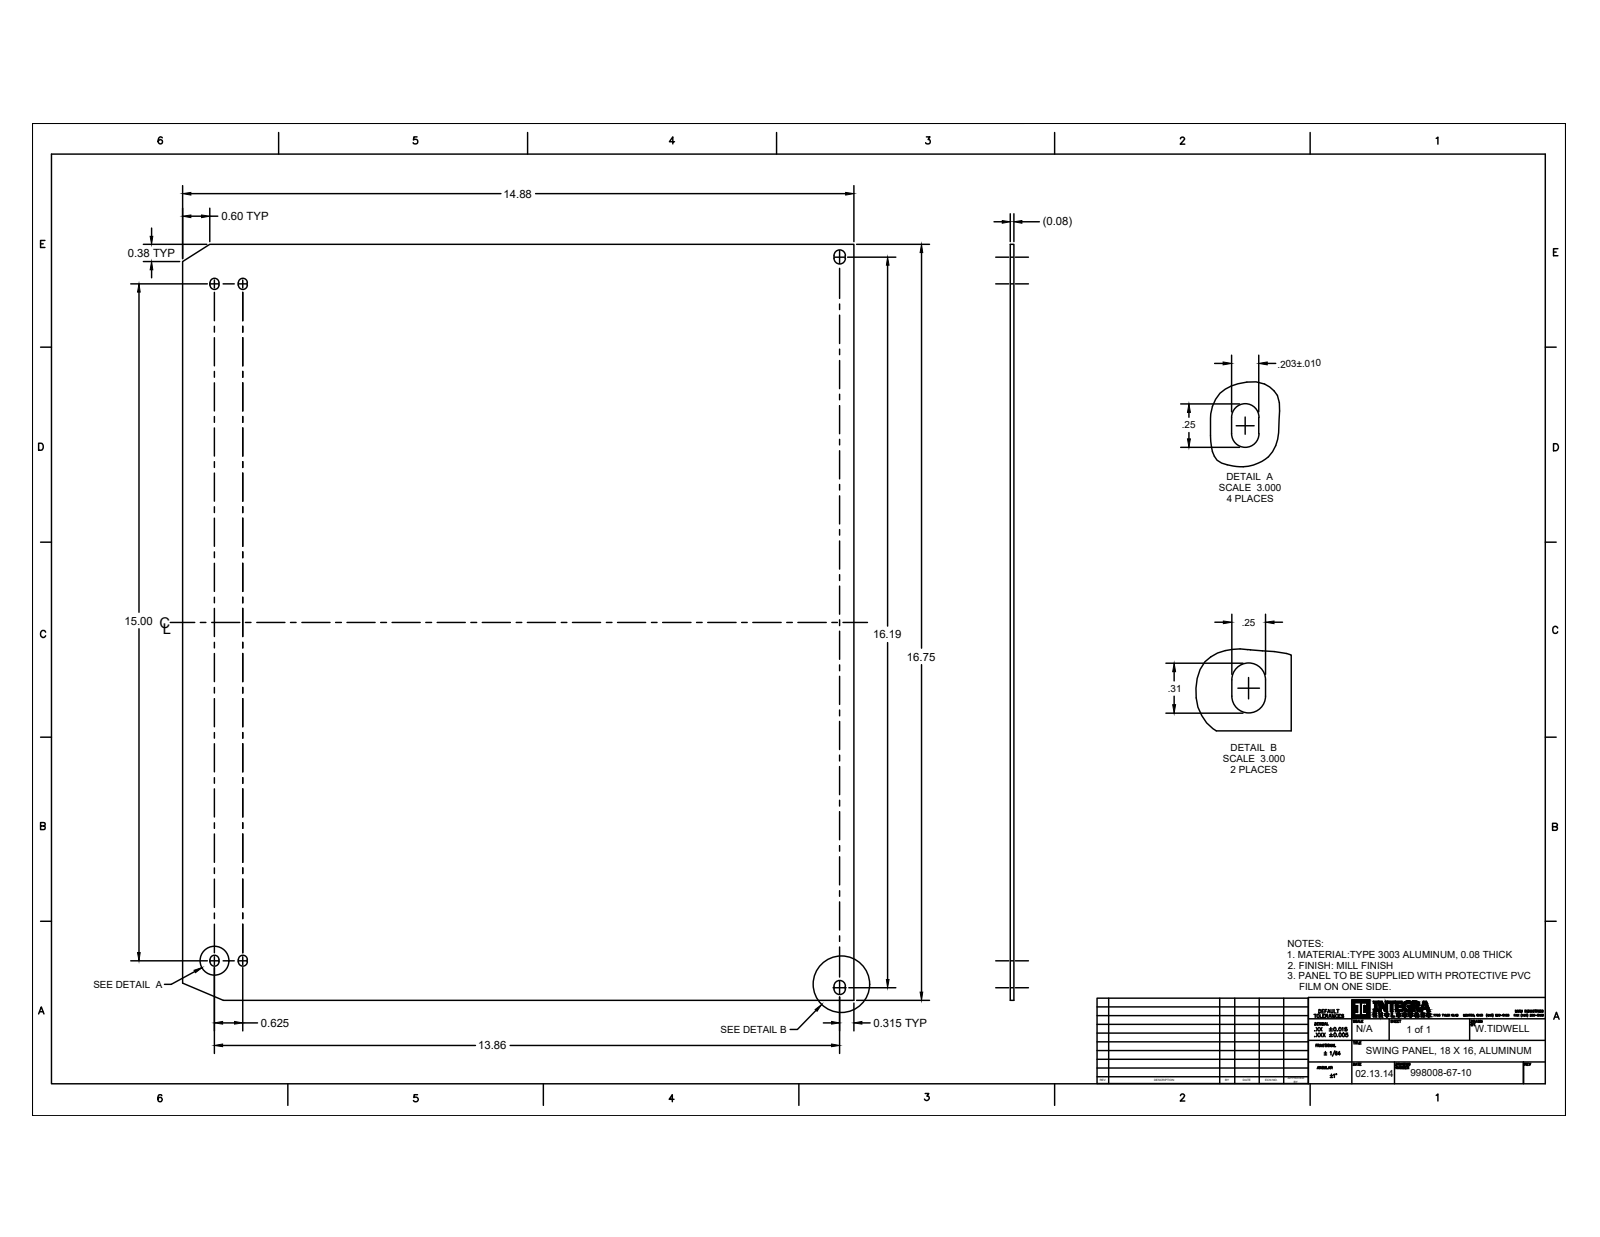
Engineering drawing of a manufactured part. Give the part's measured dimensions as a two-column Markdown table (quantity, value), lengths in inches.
| quantity | value |
| --- | --- |
| part name | ABP-1816USOPK-P10 |
| STEP written by | SolidWorks 2018 (AUTOMOTIVE_DESIGN) |
| units | inches |
| bodies | 1 solid, 32 faces (20 planar, 12 cylindrical, 0 other) |
| overall size | 16.75 × 14.88 × 0.08 |
| volume | 19.9 in³ |
| surface area | 502.9 in² |
| partial cylindrical surfaces (radius × count) | 0.101 × 8, 0.124 × 4 |
| main face-to-face distances | 0.08, 14.88, 16.75, 14.441, 14.689, 0.248, 0.439, 0.191, 0.604, 0.807 |
